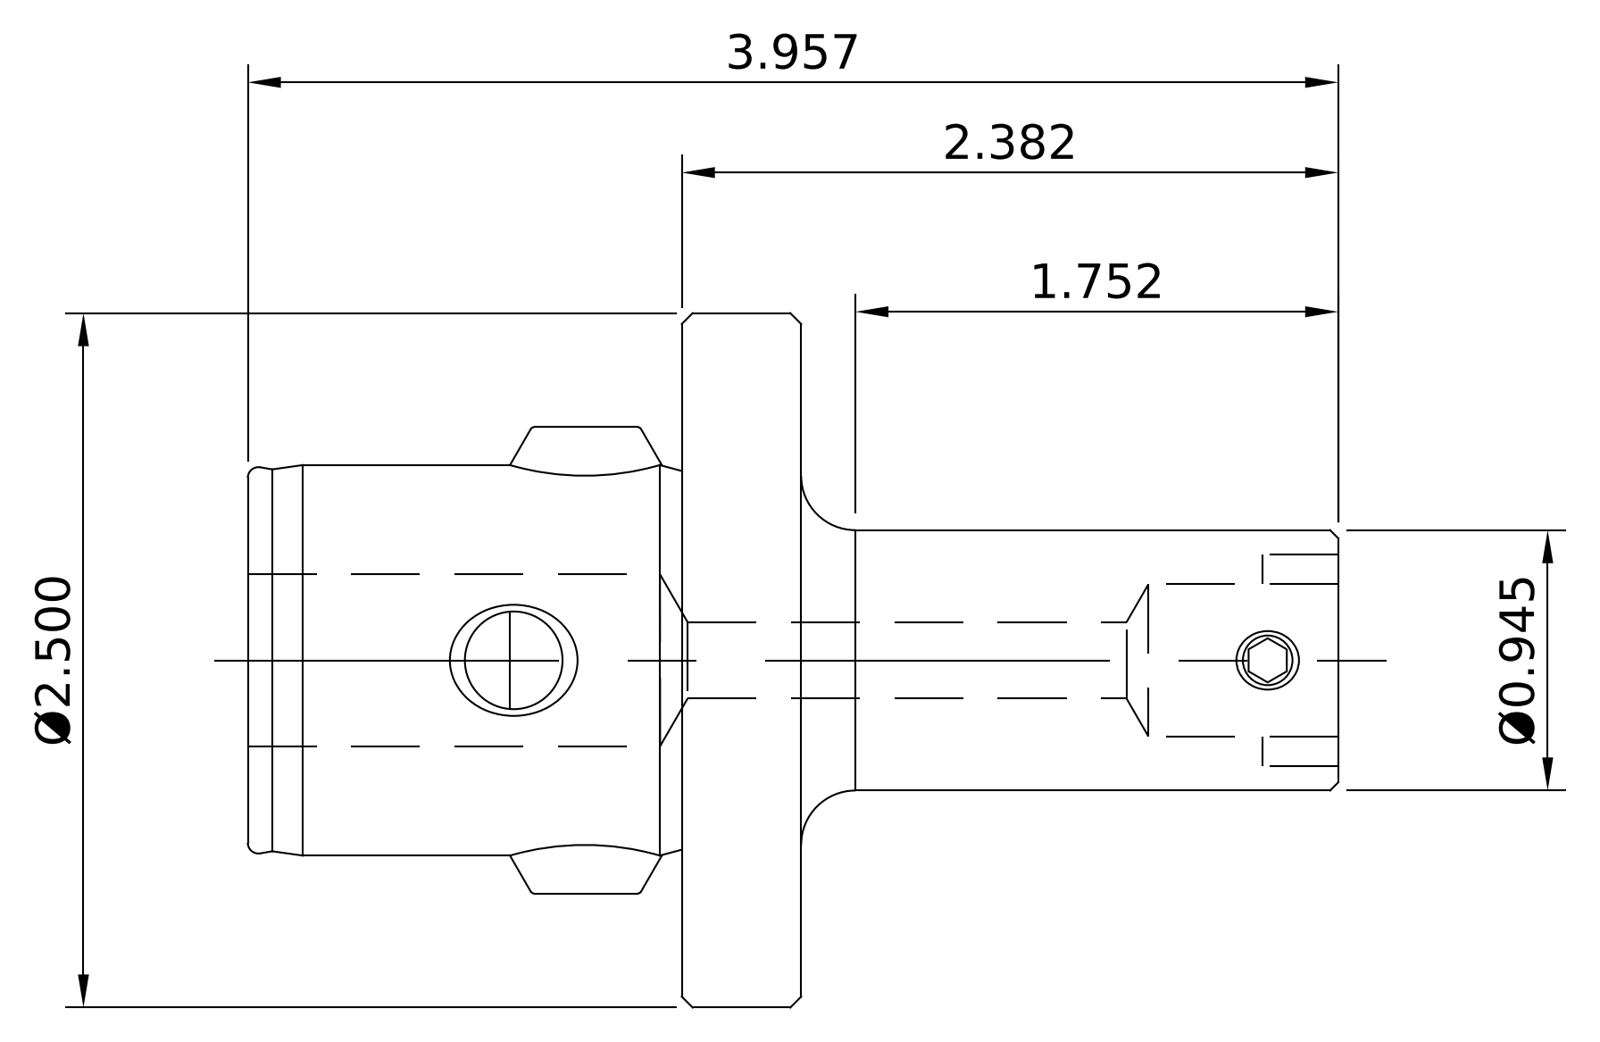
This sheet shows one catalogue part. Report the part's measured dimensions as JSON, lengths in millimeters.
{"part_name": "11.332.621", "step_written_by": "SolidWorks 2018 (CONFIG_CONTROL_DESIGN)", "units": "millimeters", "bodies": {"solids": 1, "faces": 6, "planar": 3, "cylindrical": 2, "other": 1}, "overall_size": [63.5, 63.5, 60.5], "volume_mm3": 61743, "surface_area_mm2": 12296, "round_bosses_or_shafts": [[63.5, 1], [24, 1]], "face_to_face_distances": [12.5, 60.5, 48]}
